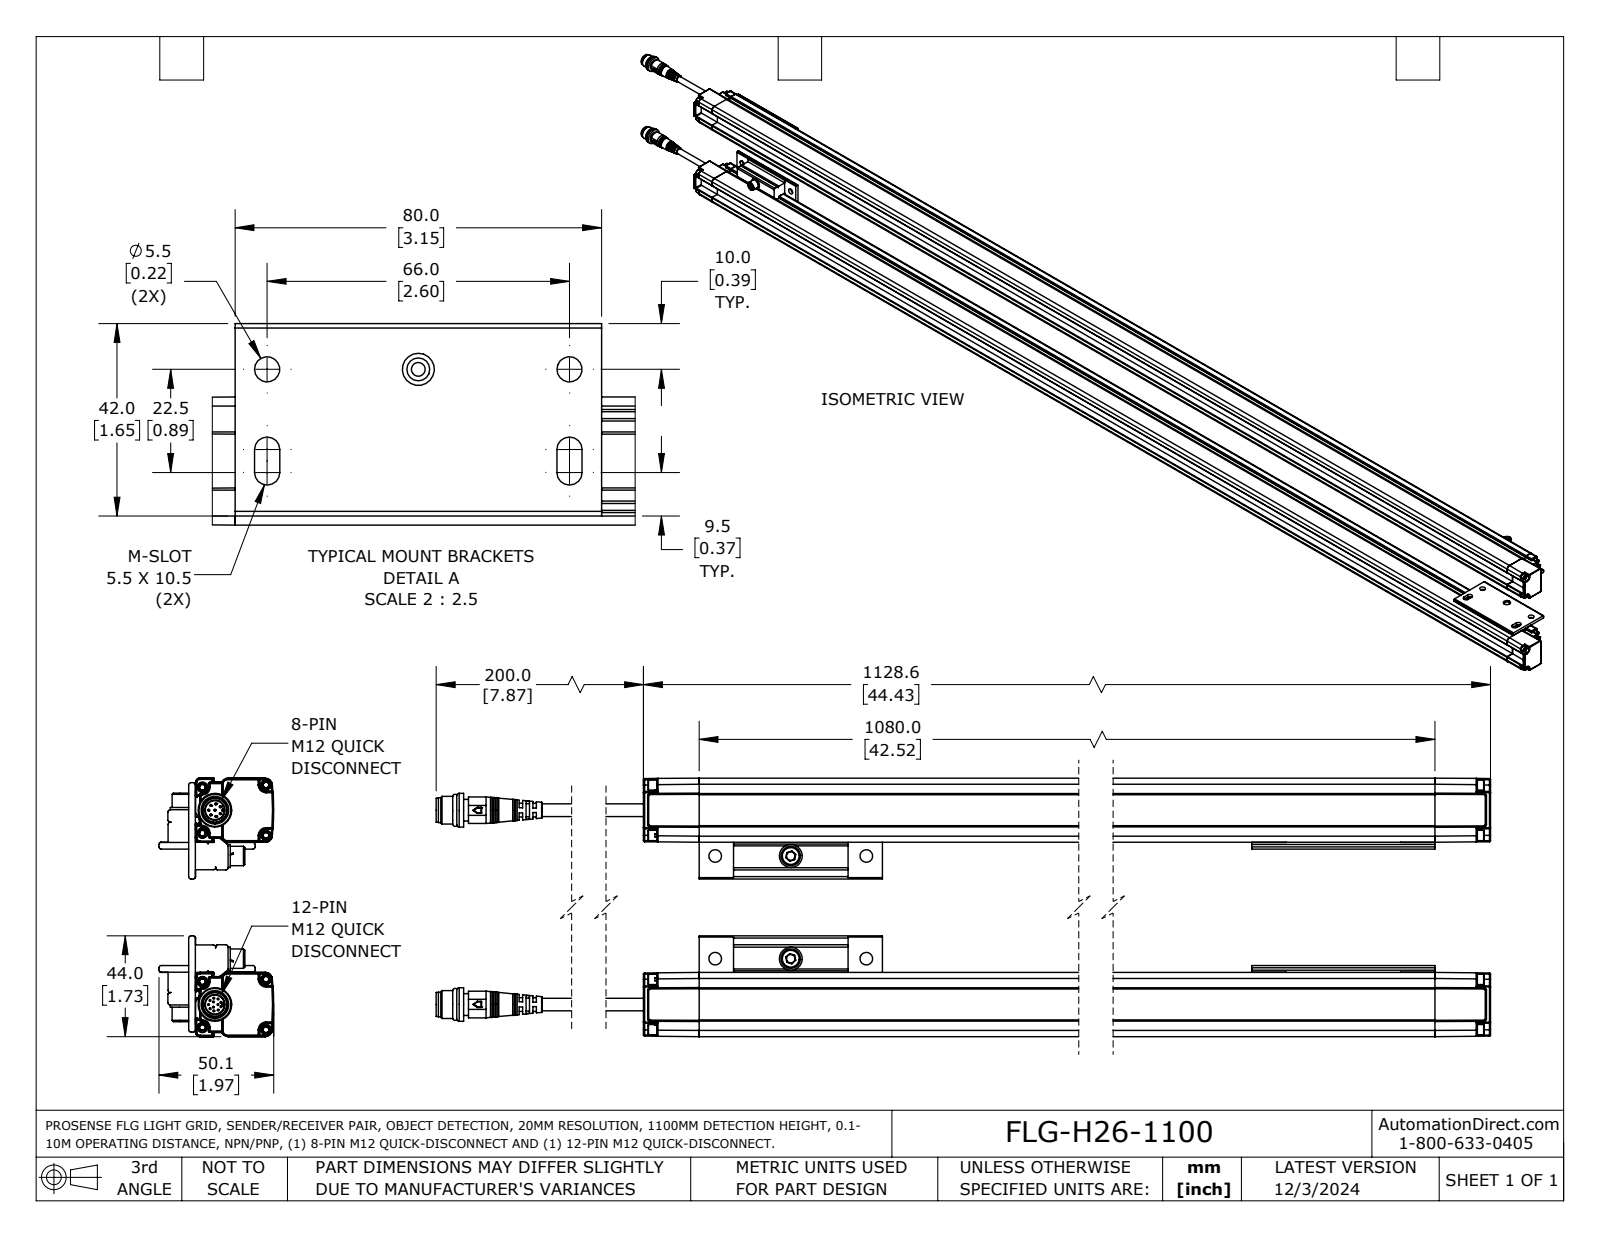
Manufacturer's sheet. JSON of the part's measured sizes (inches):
{"part_name": "FLG-H26-1100", "step_written_by": "SolidWorks 2023 (AUTOMOTIVE_DESIGN)", "units": "inches", "bodies": {"solids": 5, "faces": 869, "planar": 435, "cylindrical": 238, "other": 196}, "overall_size": [48.053, 1.972, 1.732], "volume_in3": 55.62, "surface_area_in2": 350.9, "round_holes": [[0.016, 16], [0.217, 4], [0.098, 2], [0.197, 2], [0.327, 1]], "round_bosses_or_shafts": [[0.031, 8], [0.177, 4], [0.118, 4], [0.394, 2], [0.335, 2], [0.217, 2], [0.146, 2], [0.059, 2]], "partial_cylinders_radius": [[0.02, 76], [0.039, 20], [0.01, 10], [0.108, 8], [0.008, 6], [0.012, 6], [0.1, 4], [0.049, 2]], "face_to_face_distances": [1.102, 0.071, 0.817, 0.285, 0.97, 1.041, 0.215, 1.031, 0.746, 0.531], "hole_center_spacings": [0.108, 0.163, 1.299, 0.215, 0.089, 0.09, 0.09, 0.118]}
